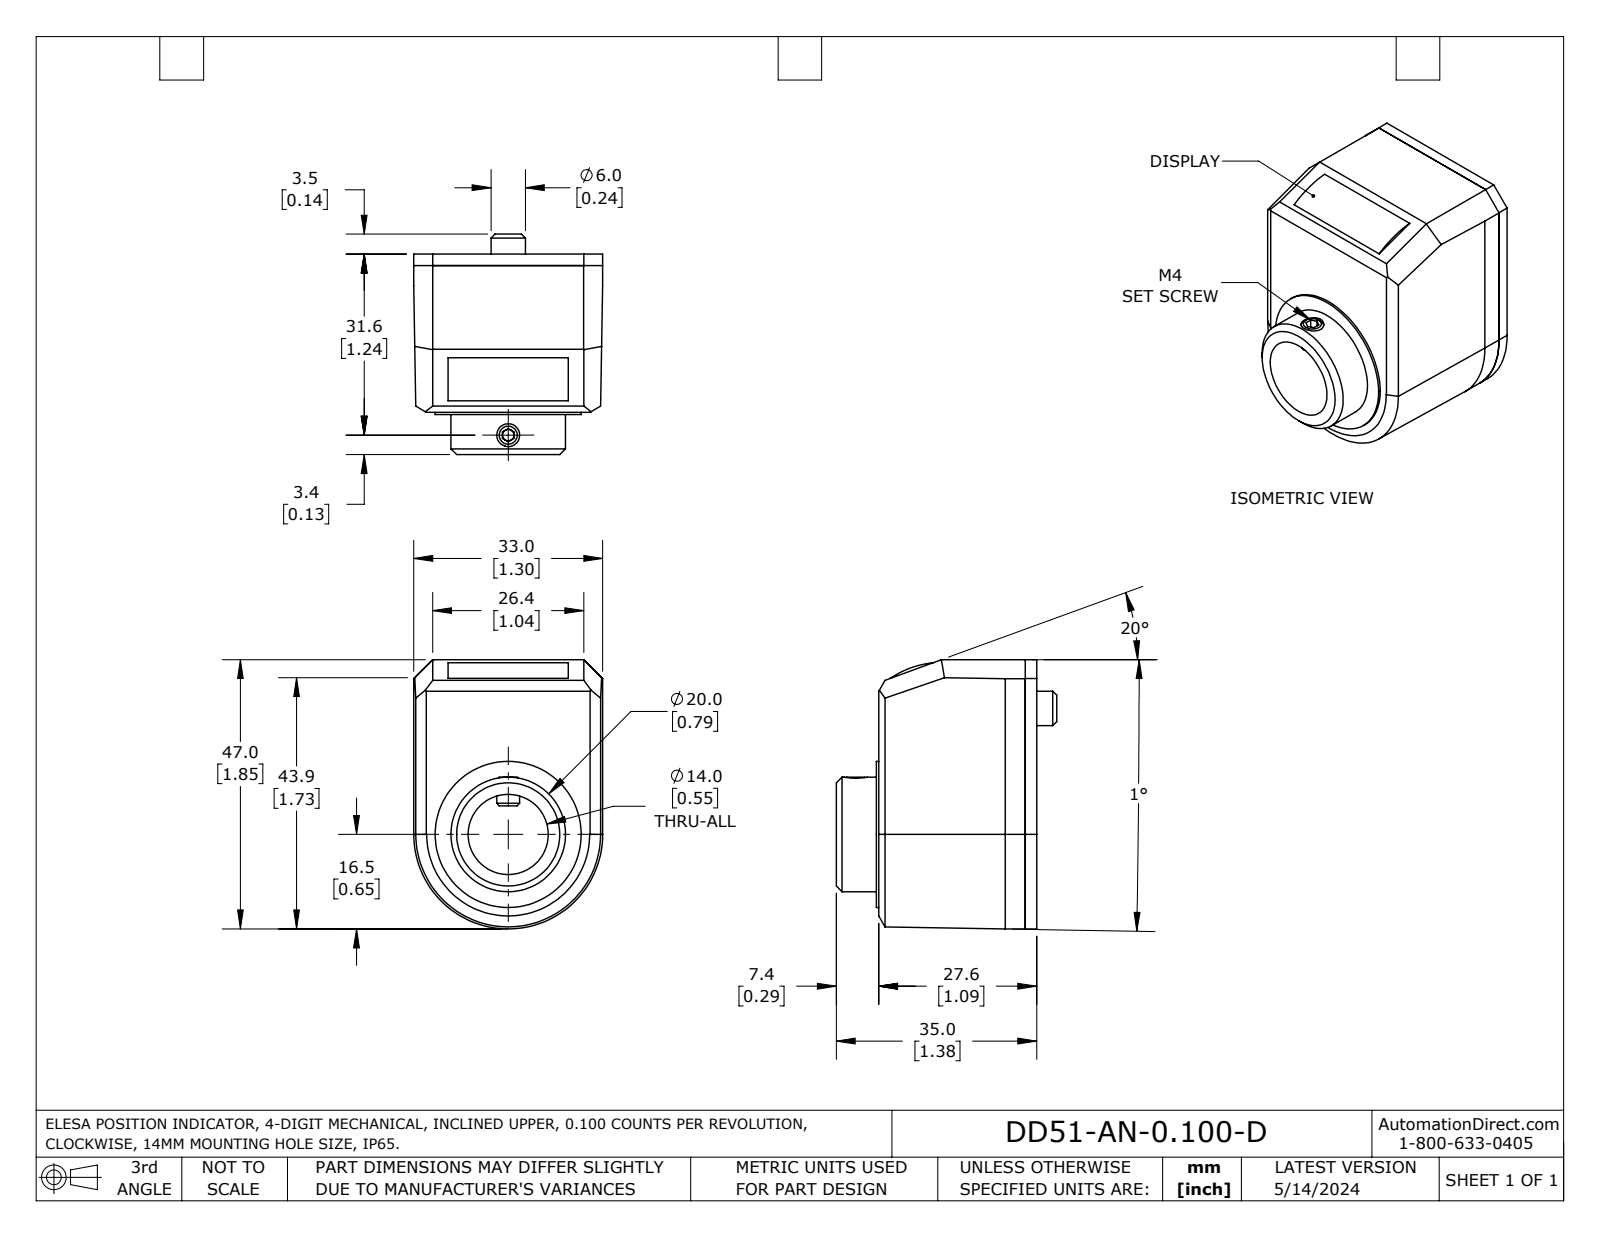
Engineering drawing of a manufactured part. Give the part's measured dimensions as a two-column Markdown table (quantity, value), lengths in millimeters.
| quantity | value |
| --- | --- |
| part name | DD51-AN-METRIC |
| STEP written by | SolidWorks 2023 (AUTOMOTIVE_DESIGN) |
| units | millimeters |
| bodies | 4 solids, 85 faces (66 planar, 12 cylindrical, 7 other) |
| overall size | 47 × 38.5 × 33 |
| volume | 32 680 mm³ |
| surface area | 13 120 mm² |
| round holes (diameter × count) | 4 × 1, 14 × 1, 20 × 1, 27.5 × 1 |
| round bosses / shafts (diameter × count) | 25.5 × 1, 6 × 1 |
| partial cylindrical surfaces (radius × count) | 16.3 × 1, 16.5 × 1 |
| main face-to-face distances | 2, 2, 25.6, 25.6, 27.6, 3.5, 5.5, 22.1, 3.5, 33 |
